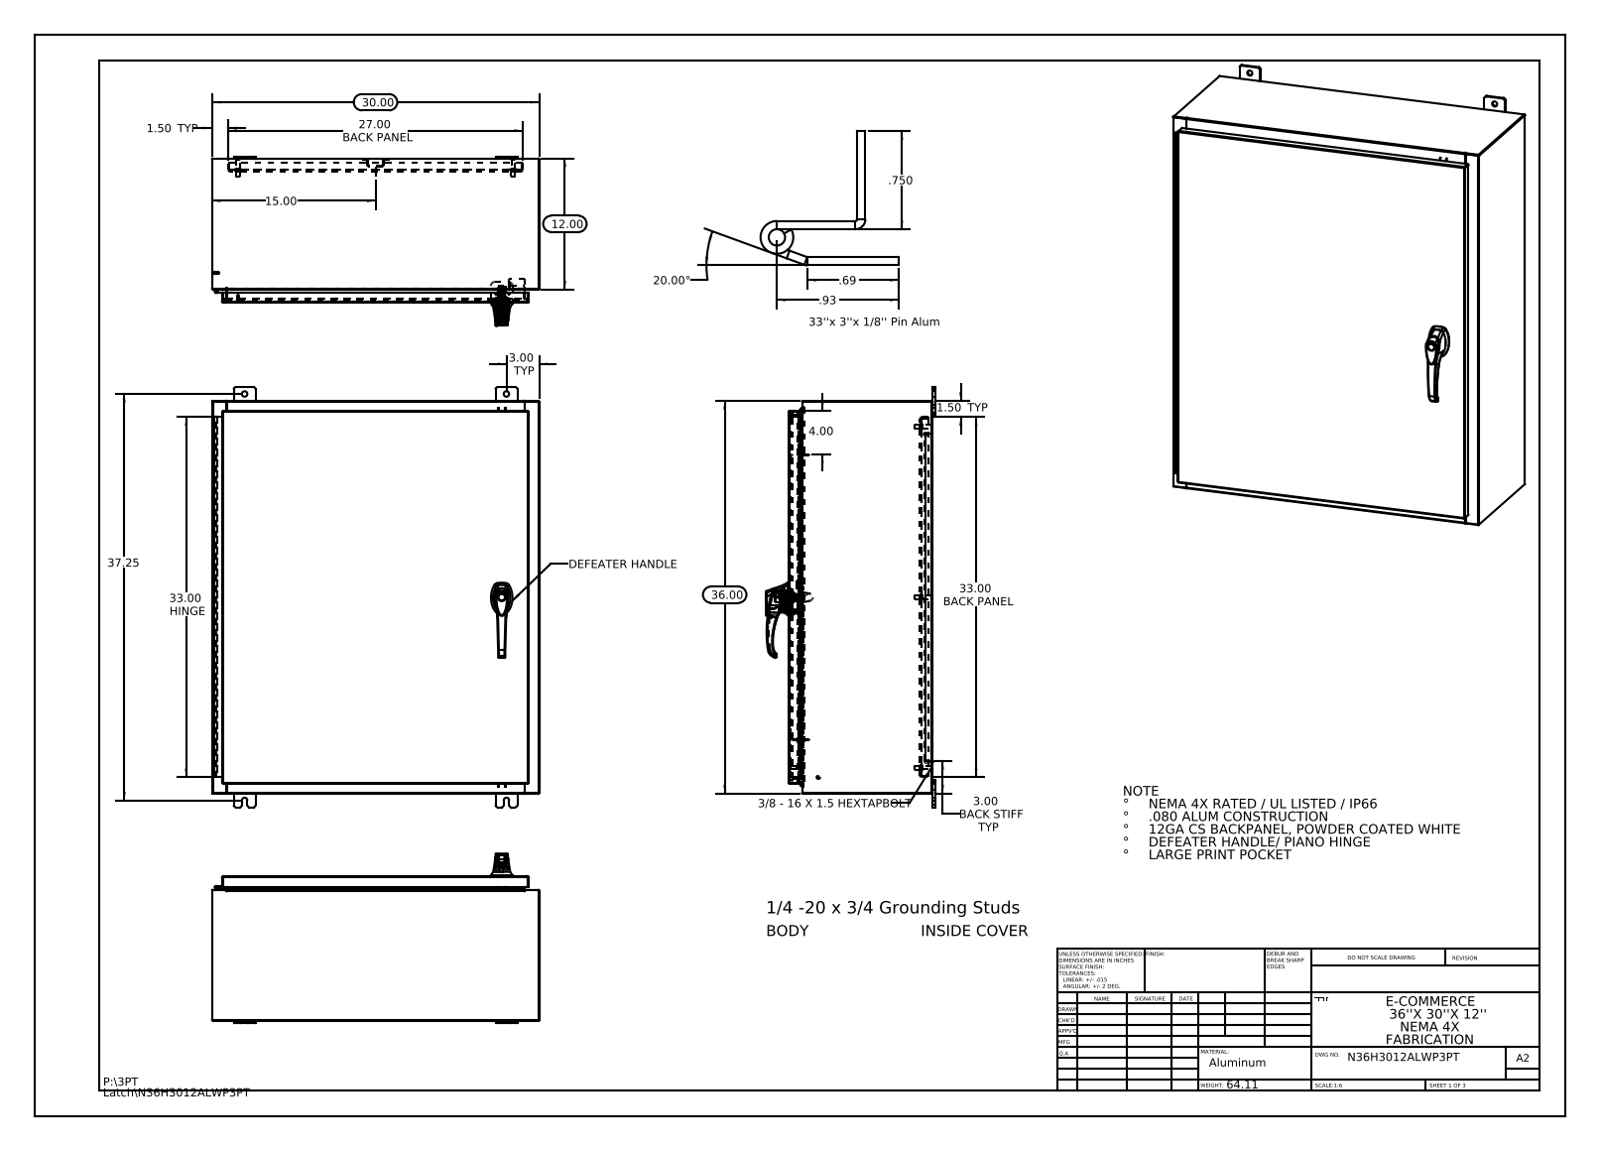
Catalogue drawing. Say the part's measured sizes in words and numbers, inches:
The part is named "26161102; 033060_032151; 00005090; N36H3012ALWP3PT (+8 more)". Its 3-D file was written by "SolidWorks 2013 (CONFIG_CONTROL_DESIGN)". It is 40 solids with 2894 faces: 1083 planar, 1093 cylindrical and 718 other. Overall it measures 38.5 by 30 by 15.495 inches. Its volume is 428.6 cubic inches and its surface area 10 658 square inches. Round holes: 10 of diameter 0.5, 4 of diameter 0.25, 3 of diameter 0.138, 3 of diameter 0.161, 2 of diameter 0.079, 2 of diameter 0.203, 2 of diameter 0.313, 2 of diameter 0.437, 1 of diameter 0.125, 1 of diameter 0.125, 1 of diameter 0.197, 1 of diameter 0.276. Round bosses or shafts: 6 of diameter 0.625, 6 of diameter 0.375, 6 of diameter 0.33, 4 of diameter 0.157, 4 of diameter 0.14, 3 of diameter 0.315, 3 of diameter 0.236, 1 of diameter 1.181. Partial cylindrical surfaces (rounded edges, fillets, slot ends): 37 of radius 0.118, 33 of radius 0.006, 28 of radius 0.013, 24 of radius 0.19, 22 of radius 0.088, 15 of radius 0.039, 12 of radius 0.028, 6 of radius 0.008. The main face-to-face distances are 0.075, 13.126, 13.051, 0.104, 13.201, 1, 12.126, 1.075, 12.051, 1.179. The hole center spacings are 11.363, 13.669, 15.625, 29.694, 25.25, 28.129, 0.295, 0.625.
